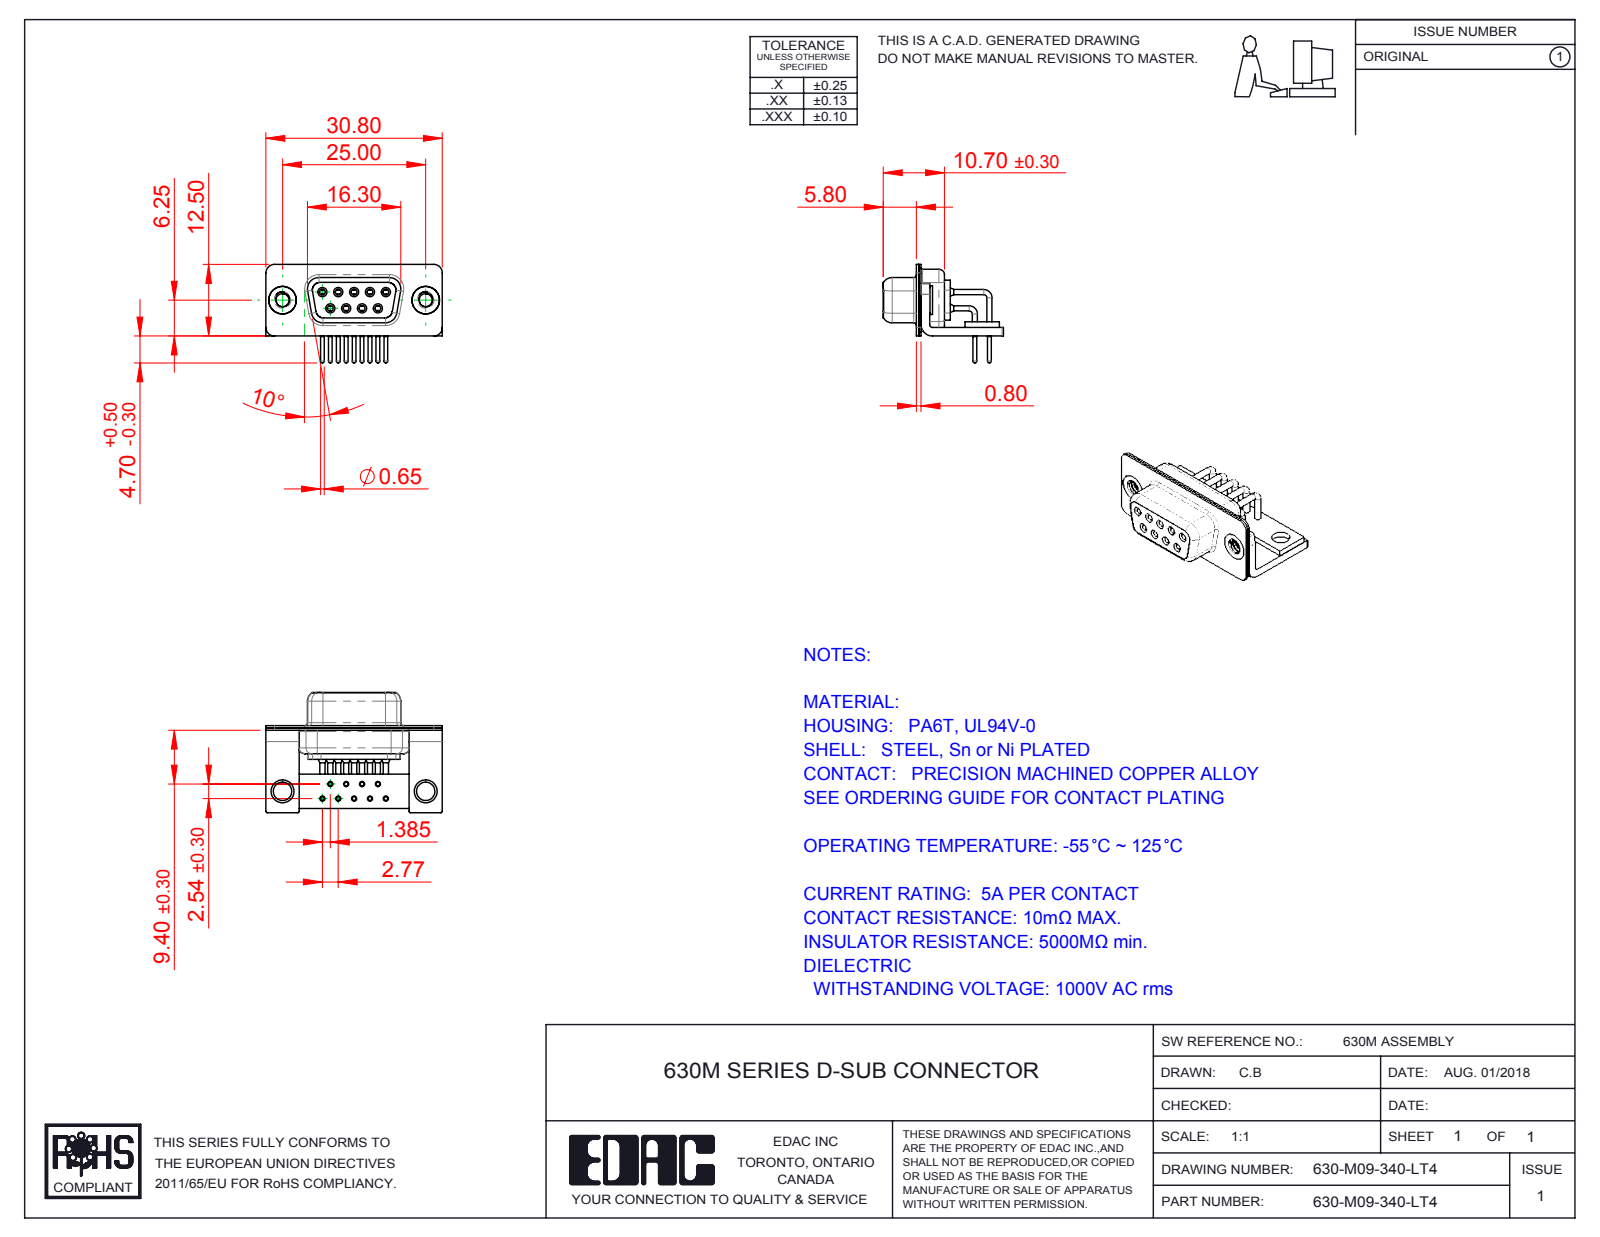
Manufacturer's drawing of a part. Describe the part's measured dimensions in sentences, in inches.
The part is named "630M Shell Front_09 Contacts; 630M Shell Rear_09 Contacts; 630-M09-340-LT4; 630M Contact Row 1 (+5 more)". Its 3-D file was written by "SolidWorks 2016 (CONFIG_CONTROL_DESIGN)". It is 17 solids with 824 faces: 228 planar, 384 cylindrical and 212 other. Overall it measures 1.213 by 0.827 by 0.677 inches. Its volume is 0.134 cubic inches and its surface area 8.795 square inches. Round holes: 9 of diameter 0.035, 9 of diameter 0.039, 9 of diameter 0.043, 9 of diameter 0.067, 9 of diameter 0.071, 9 of diameter 0.079, 2 of diameter 0.089, 2 of diameter 0.126, 2 of diameter 0.157, 2 of diameter 0.189. Round bosses or shafts: 9 of diameter 0.063, 9 of diameter 0.059, 9 of diameter 0.035, 9 of diameter 0.026, 2 of diameter 0.197, 2 of diameter 0.193. Partial cylindrical surfaces (rounded edges, fillets, slot ends): 16 of radius 0.01, 16 of radius 0.059, 13 of radius 0.079, 8 of radius 0.053, 8 of radius 0.063, 5 of radius 0.02, 4 of radius 0.024, 4 of radius 0.026. The main face-to-face distances are 0.016, 0.031, 0.059, 0.091, 0.075, 0.039, 0.368, 0.057, 0.098, 0.352. The hole center spacings are 0.109, 0.218, 0.124, 0.192, 0.327, 0.114, 0.114, 0.198.
